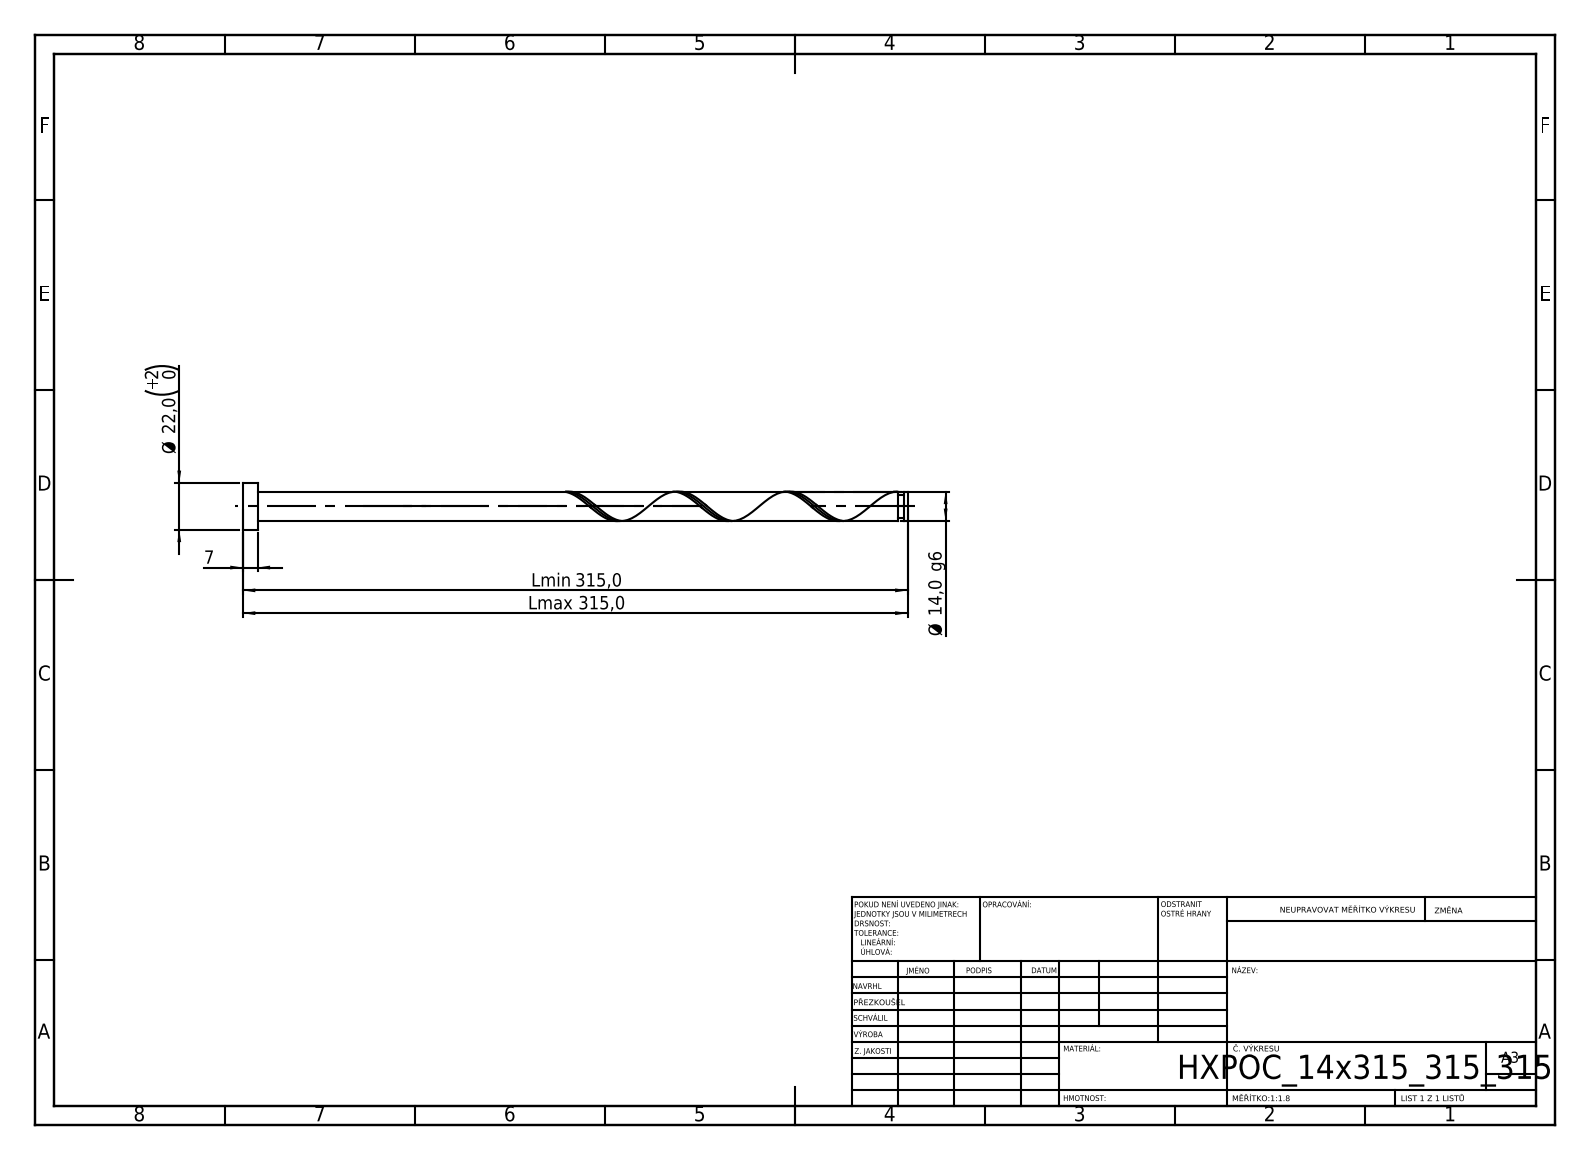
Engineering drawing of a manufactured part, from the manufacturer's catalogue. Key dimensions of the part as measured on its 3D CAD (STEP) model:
STEP written by: SolidWorks 2019 (CONFIG_CONTROL_DESIGN)
Units: millimetres
Bodies: 1 solid, 21 faces (6 planar, 14 cylindrical, 1 other)
Overall size (bounding box): 315 × 22 × 22
Volume: 49 454 mm³ · Surface area: 15 179 mm²
Round bosses / shafts (diameter × count): ⌀22 ×1, ⌀14 ×1, ⌀11.2 ×1
Main face-to-face distances: 7, 315, 308, 313.06, 306.06, 1.94, 310.26, 303.26, 2.8, 4.74
